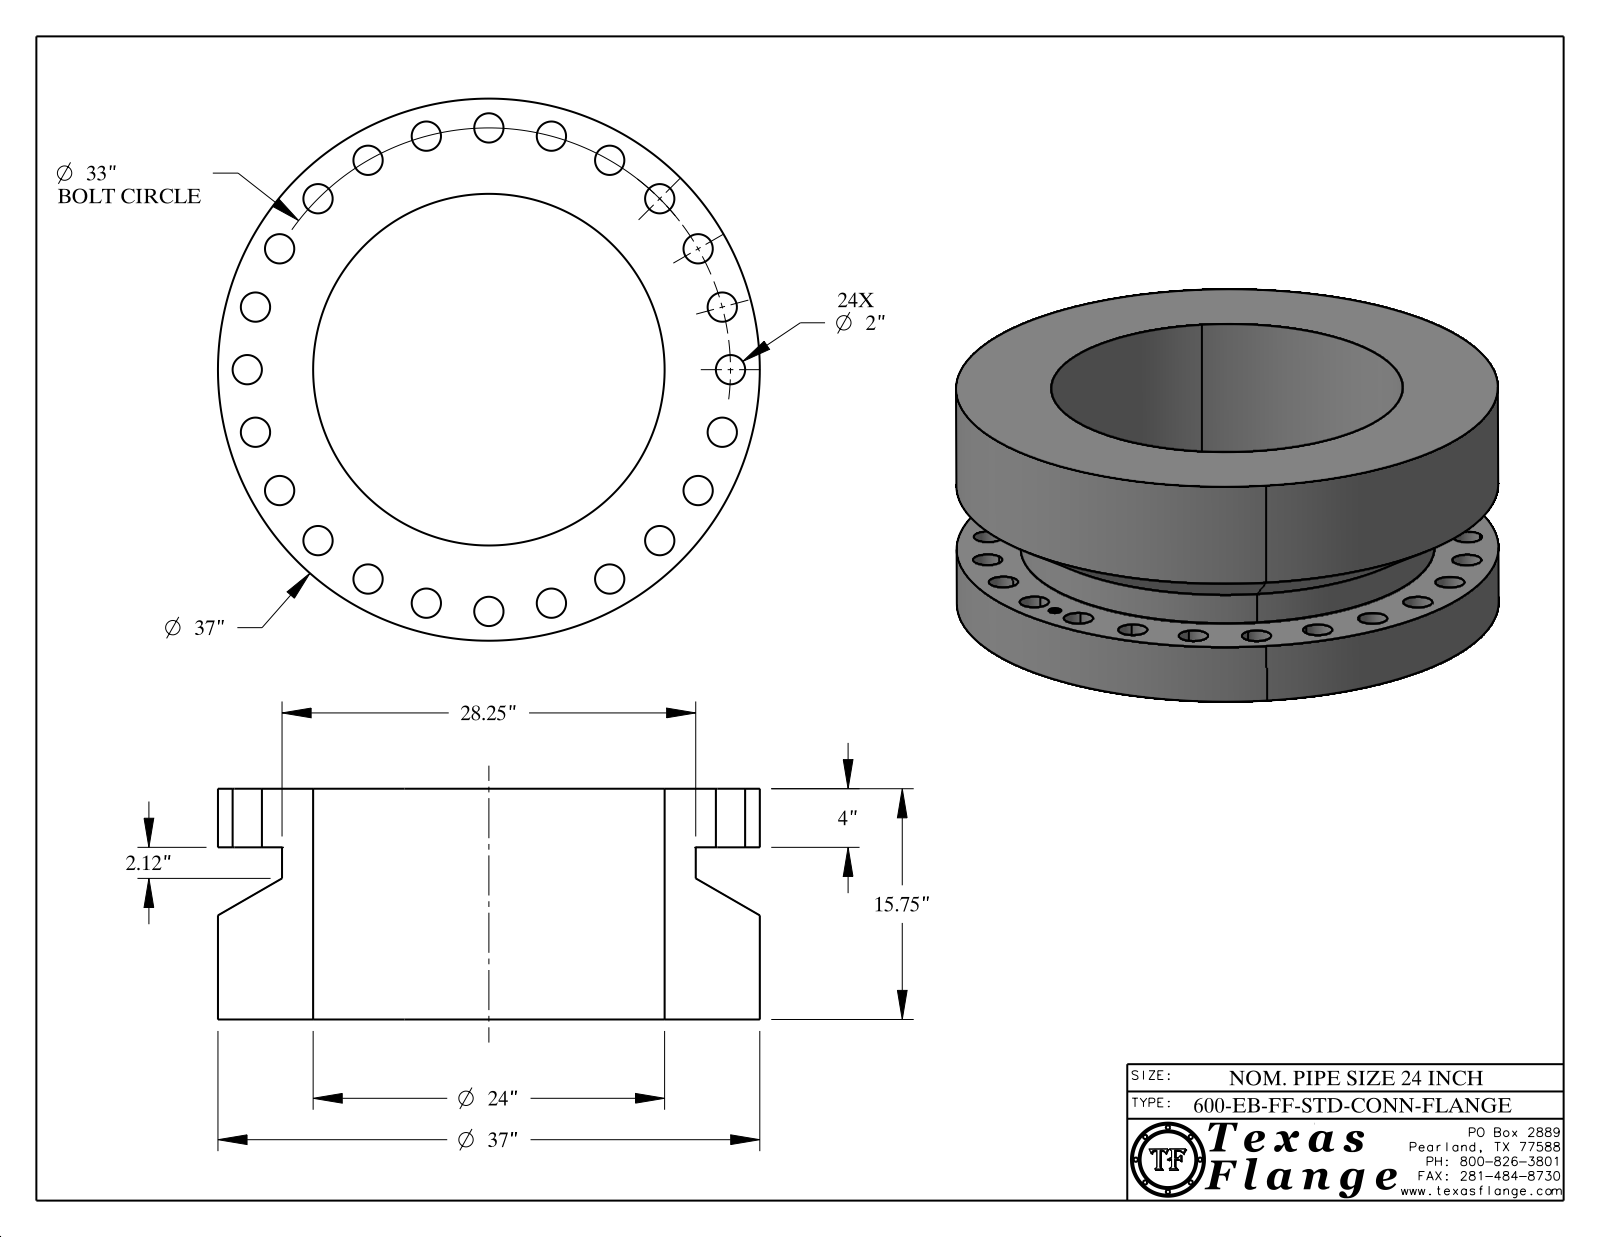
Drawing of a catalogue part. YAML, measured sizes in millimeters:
part_name: "24-600-EB-FF-STD-CONN-FLANGE"
step_written_by: "CATIA V5 STEP AP214 (AUTOMOTIVE_DESIGN)"
units: millimeters
bodies: {solids: 1, faces: 450, planar: 368, cylindrical: 76, other: 6}
overall_size: [939.8, 939.8, 400.1]
volume: 130500000
surface_area: 3441000
round_holes:
  - {diameter: 50.8, count: 24}
  - {diameter: 21.6, count: 1}
  - {diameter: 609.6, count: 1}
round_bosses_or_shafts:
  - {diameter: 1.3, count: 8}
  - {diameter: 939.8, count: 1}
  - {diameter: 717.6, count: 1}
  - {diameter: 17, count: 1}
face_to_face_distances: [400.1, 101.6, 298.5, 101.5, 298.6, 0.4, 6.5, 6.3, 1.2, 4.2]
hole_center_spacings: [419.1, 109.4, 216.9, 510.3, 592.7, 665, 809.7, 831]
